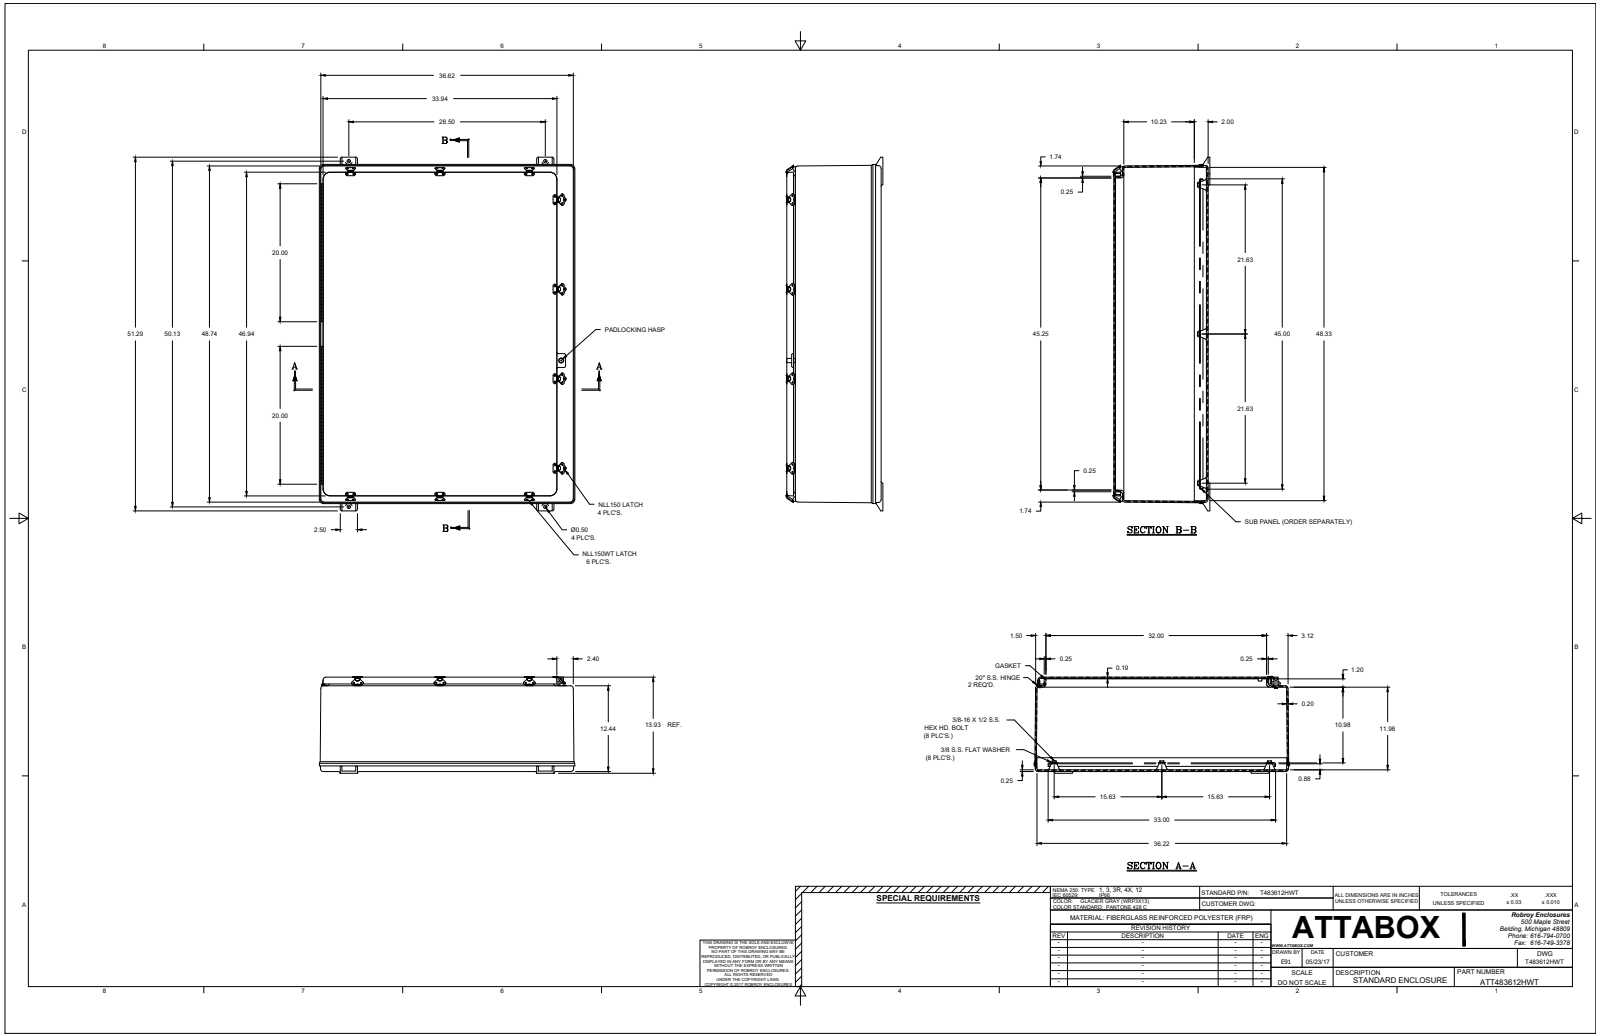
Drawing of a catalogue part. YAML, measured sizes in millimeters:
part_name: "T483612HWT"
step_written_by: "SolidWorks 2018 (AUTOMOTIVE_DESIGN)"
units: millimeters
bodies: {solids: 121, faces: 3002, planar: 1131, cylindrical: 1226, other: 645}
overall_size: [1302.5, 941.4, 362.1]
volume: 21680000
surface_area: 8323000
round_holes:
  - {diameter: 3.3, count: 76}
  - {diameter: 1.6, count: 40}
  - {diameter: 3.5, count: 20}
  - {diameter: 4.7, count: 20}
  - {diameter: 1.7, count: 8}
  - {diameter: 1.7, count: 8}
  - {diameter: 14.3, count: 8}
  - {diameter: 3.4, count: 3}
  - {diameter: 4, count: 3}
  - {diameter: 3.7, count: 2}
  - {diameter: 7.1, count: 2}
  - {diameter: 13, count: 2}
round_bosses_or_shafts:
  - {diameter: 3.6, count: 40}
  - {diameter: 7.5, count: 16}
  - {diameter: 12.7, count: 10}
  - {diameter: 5.1, count: 3}
  - {diameter: 6.4, count: 1}
  - {diameter: 5.1, count: 1}
  - {diameter: 3.4, count: 1}
partial_cylinders:
  - {radius: 0.3, count: 217}
  - {radius: 0.8, count: 40}
  - {radius: 7.9, count: 33}
  - {radius: 6.4, count: 24}
  - {radius: 5.3, count: 20}
  - {radius: 30.1, count: 20}
  - {radius: 9.5, count: 18}
  - {radius: 1.6, count: 12}
face_to_face_distances: [5.2, 6.4, 4.8, 347.3, 340.9, 342.5, 336.2, 316.3, 31, 311.2]
hole_center_spacings: [312.8, 25.4, 158.8, 161.9, 161.9, 277.8, 320.7, 320.7]
